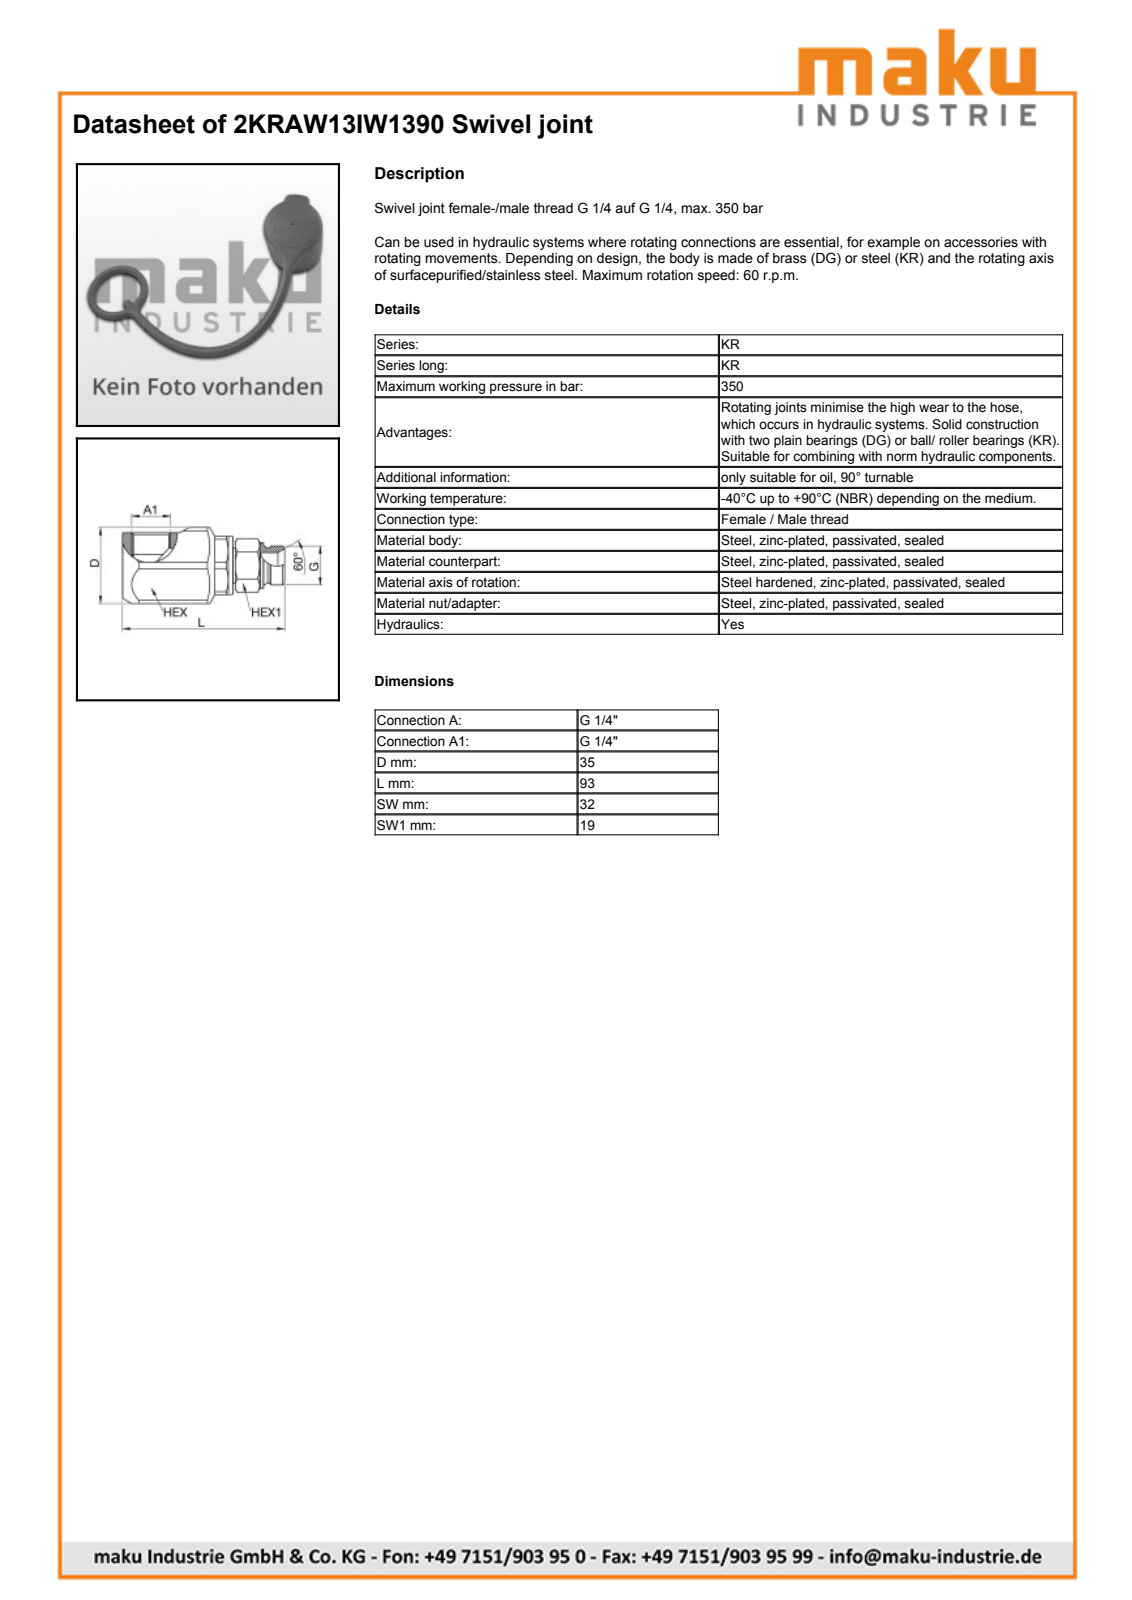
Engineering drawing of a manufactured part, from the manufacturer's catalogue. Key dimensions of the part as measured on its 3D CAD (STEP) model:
Part name (STEP PRODUCT): 2KRAW13IW1390
STEP written by: SolidWorks 2007 (AUTOMOTIVE_DESIGN)
Units: millimetres
Bodies: 1 solid, 129 faces (35 planar, 39 cylindrical, 55 other)
Overall size (bounding box): 92.5 × 35 × 32
Volume: 52 096 mm³ · Surface area: 11 477 mm²
Round holes (diameter × count): ⌀6 ×1, ⌀9.8 ×1, ⌀11.45 ×1, ⌀12.4 ×1, ⌀16 ×1, ⌀16.9 ×1, ⌀24.2 ×1
Round bosses / shafts (diameter × count): ⌀26.7 ×1, ⌀24 ×1, ⌀18 ×1, ⌀13.16 ×1, ⌀11.9 ×1, ⌀11.4 ×1
Partial cylindrical surfaces — rounded edges, fillets, slot ends (radius × count): R14.5 ×1, R17.5 ×1
Main face-to-face distances: 32, 2.5, 29.5, 19, 30, 61.3, 27, 2, 63.5, 2.2
